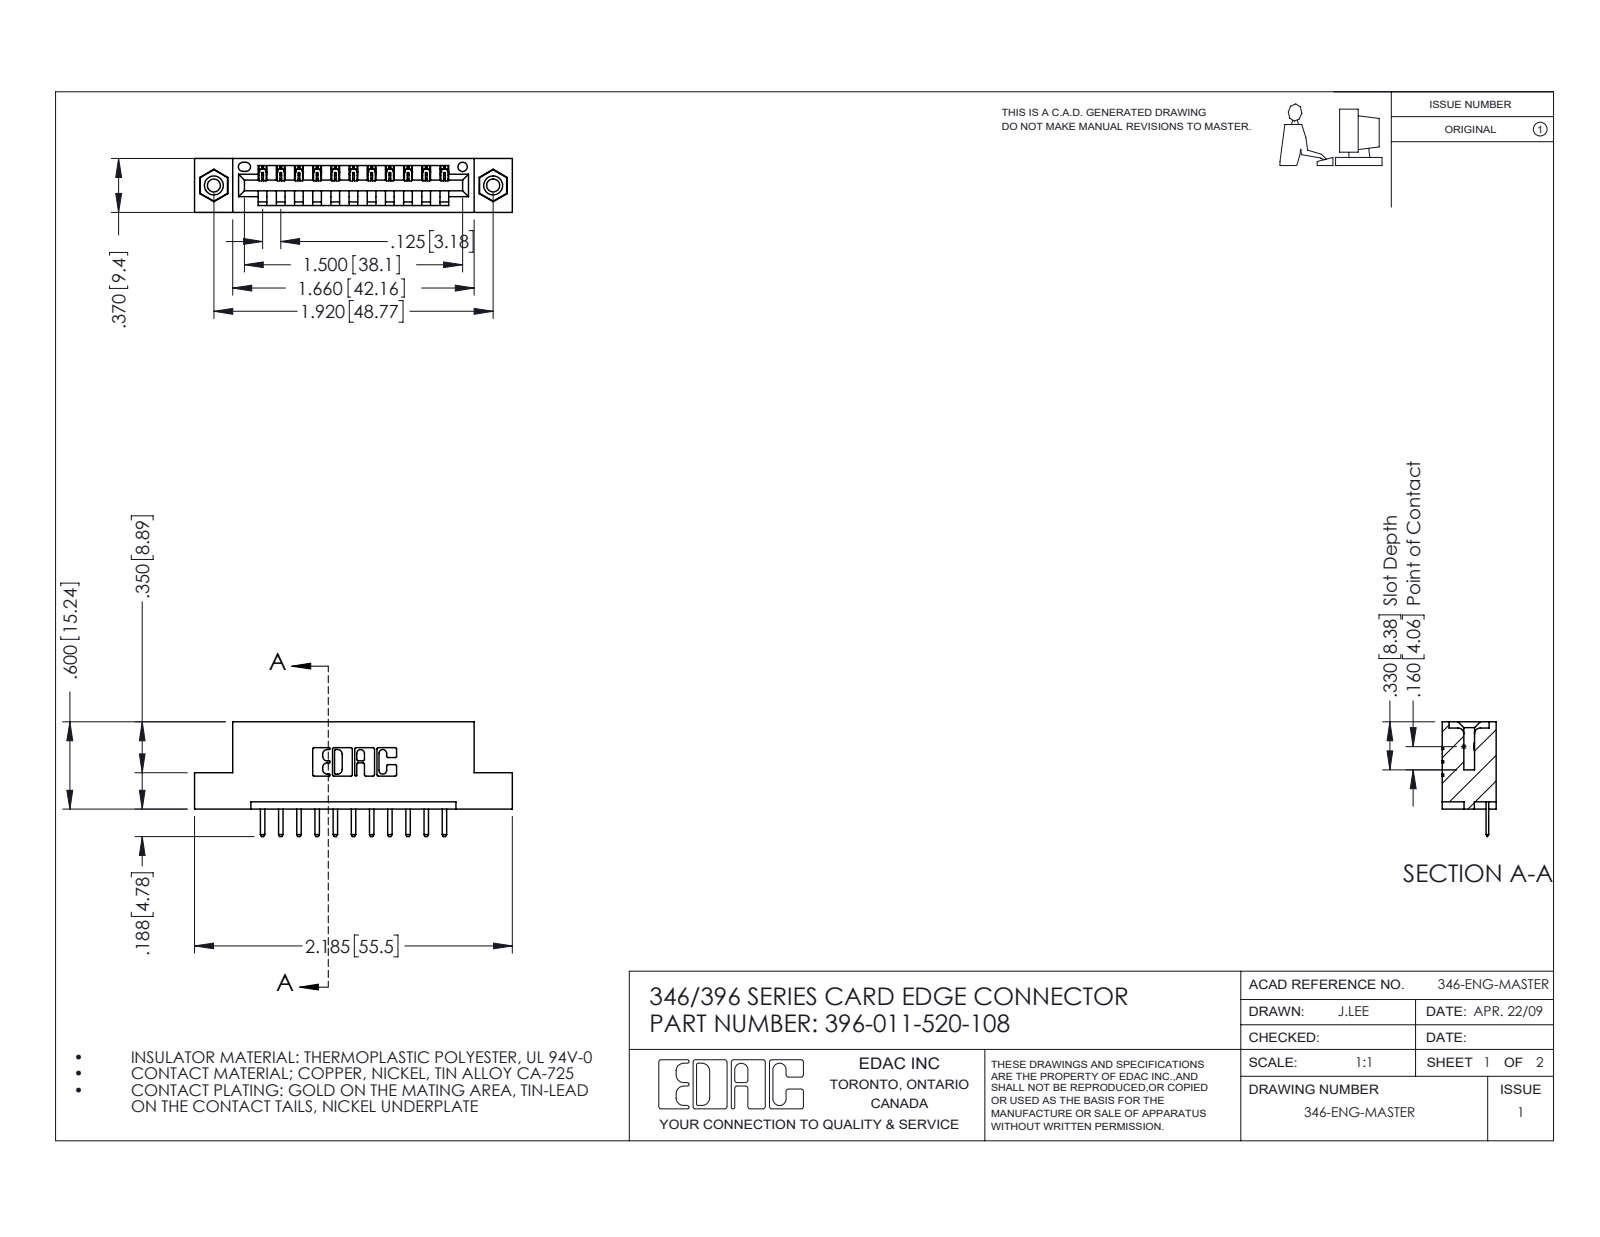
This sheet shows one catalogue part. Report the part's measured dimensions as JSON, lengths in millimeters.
{"part_name": "396-011-520-108; 345-292-001_345-293-120; 345-250-001_345-250-003-102; 346 Part_Flush Mounting Lugs - 0.156 Dia-TI", "step_written_by": "SolidWorks 2016 (CONFIG_CONTROL_DESIGN)", "units": "millimeters", "bodies": {"solids": 14, "faces": 864, "planar": 570, "cylindrical": 278, "other": 16}, "overall_size": [55.5, 20, 9.4], "volume_mm3": 5060, "surface_area_mm2": 5907, "round_holes": [[2.3, 2], [3.2, 2], [4, 2], [1.6, 1]], "round_bosses_or_shafts": [[3.9, 2]], "partial_cylinders_radius": [[0.3, 24], [0.2, 22], [0.3, 22], [0.2, 6], [0.8, 6], [0.7, 3], [0.8, 2], [1, 2]], "face_to_face_distances": [6.4, 9.4, 1.2, 8.2, 3.8, 5.6, 2.5, 4.4, 1.8, 7.6], "hole_center_spacings": [6.2, 43.6, 48.8]}
